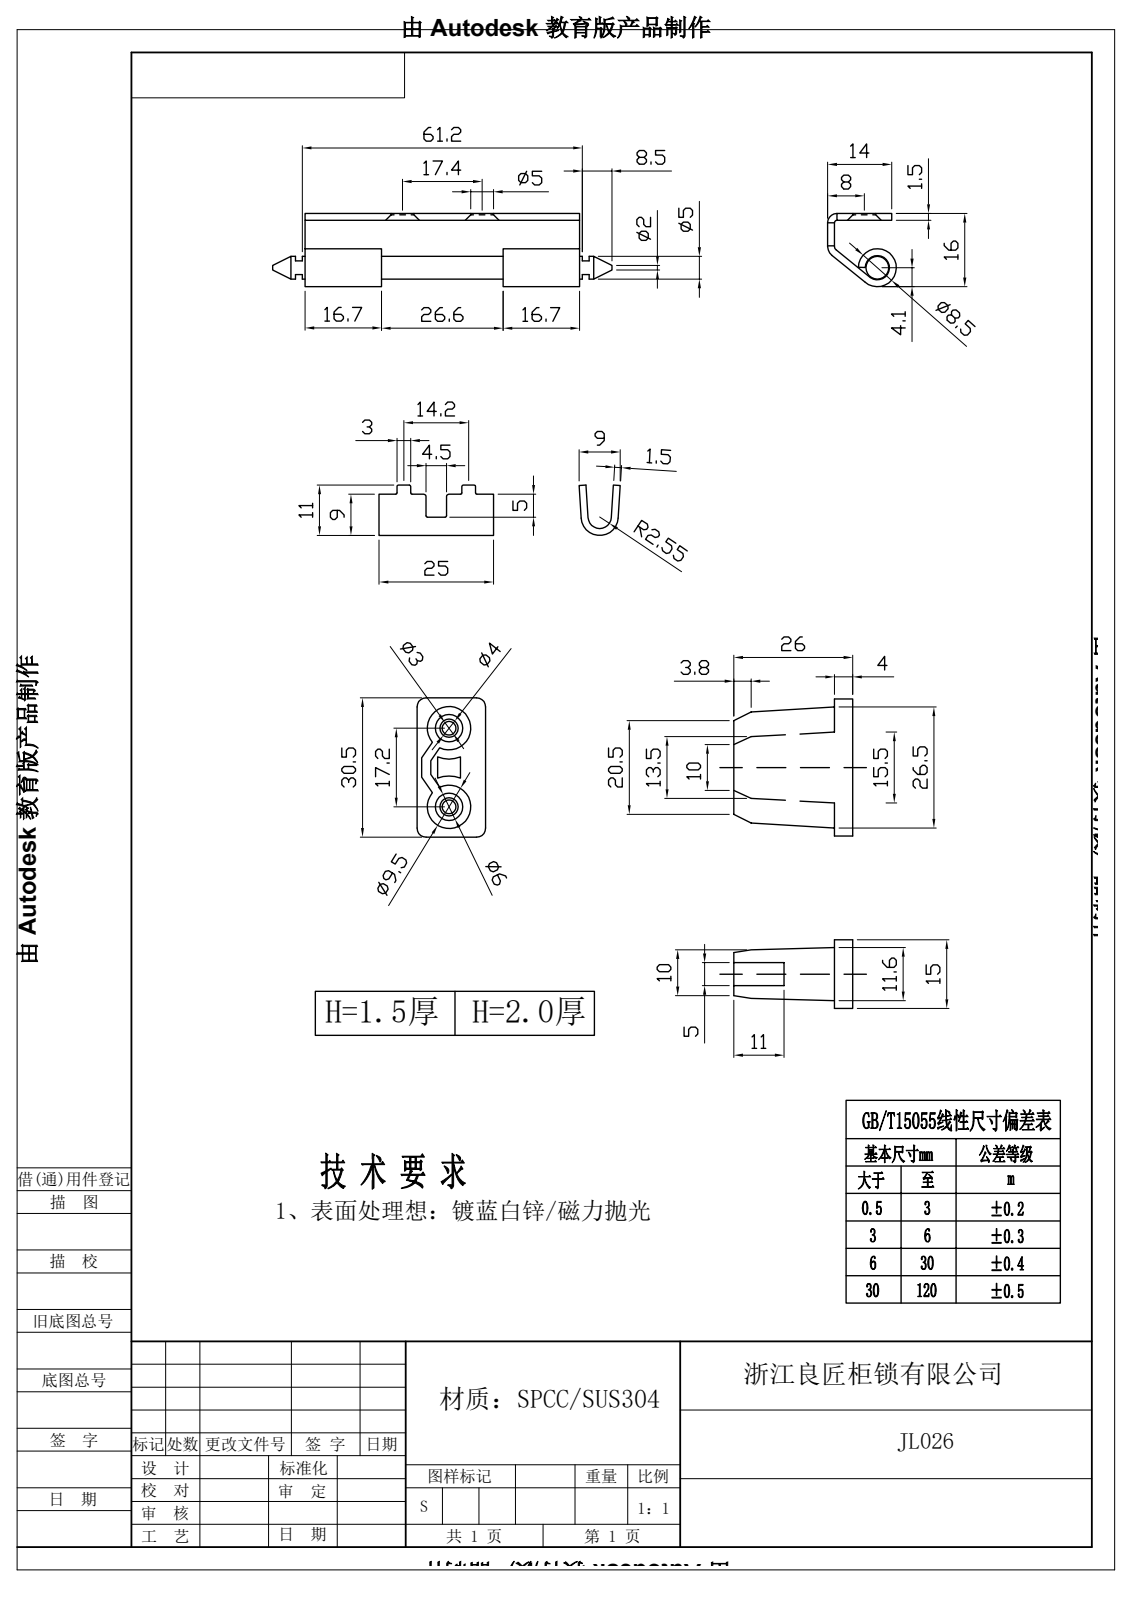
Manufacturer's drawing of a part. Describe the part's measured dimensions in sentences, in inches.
Its 3-D file was written by "Rhino 8.5 (CONFIG_CONTROL_DESIGN)". It is 3 solids with 88 faces: 56 planar, 24 cylindrical and 8 other. Overall it measures 3.988 by 0.635 by 0.591 inches. Its volume is 0.334 cubic inches and its surface area 11.37 square inches. Round holes: 2 of diameter 0.197, 1 of diameter 0.209. Round bosses or shafts: 1 of diameter 0.327, 1 of diameter 0.197, 1 of diameter 0.118. Partial cylindrical surfaces (rounded edges, fillets, slot ends): 1 of radius 0.02, 1 of radius 0.039, 1 of radius 0.079, 1 of radius 0.098, 1 of radius 0.1, 1 of radius 0.159. The main face-to-face distances are 0.059, 0.492, 0.551, 2.362, 0.657, 1.705, 0.264, 0.205, 0.287, 0.402. The hole center spacings are 0.685.
